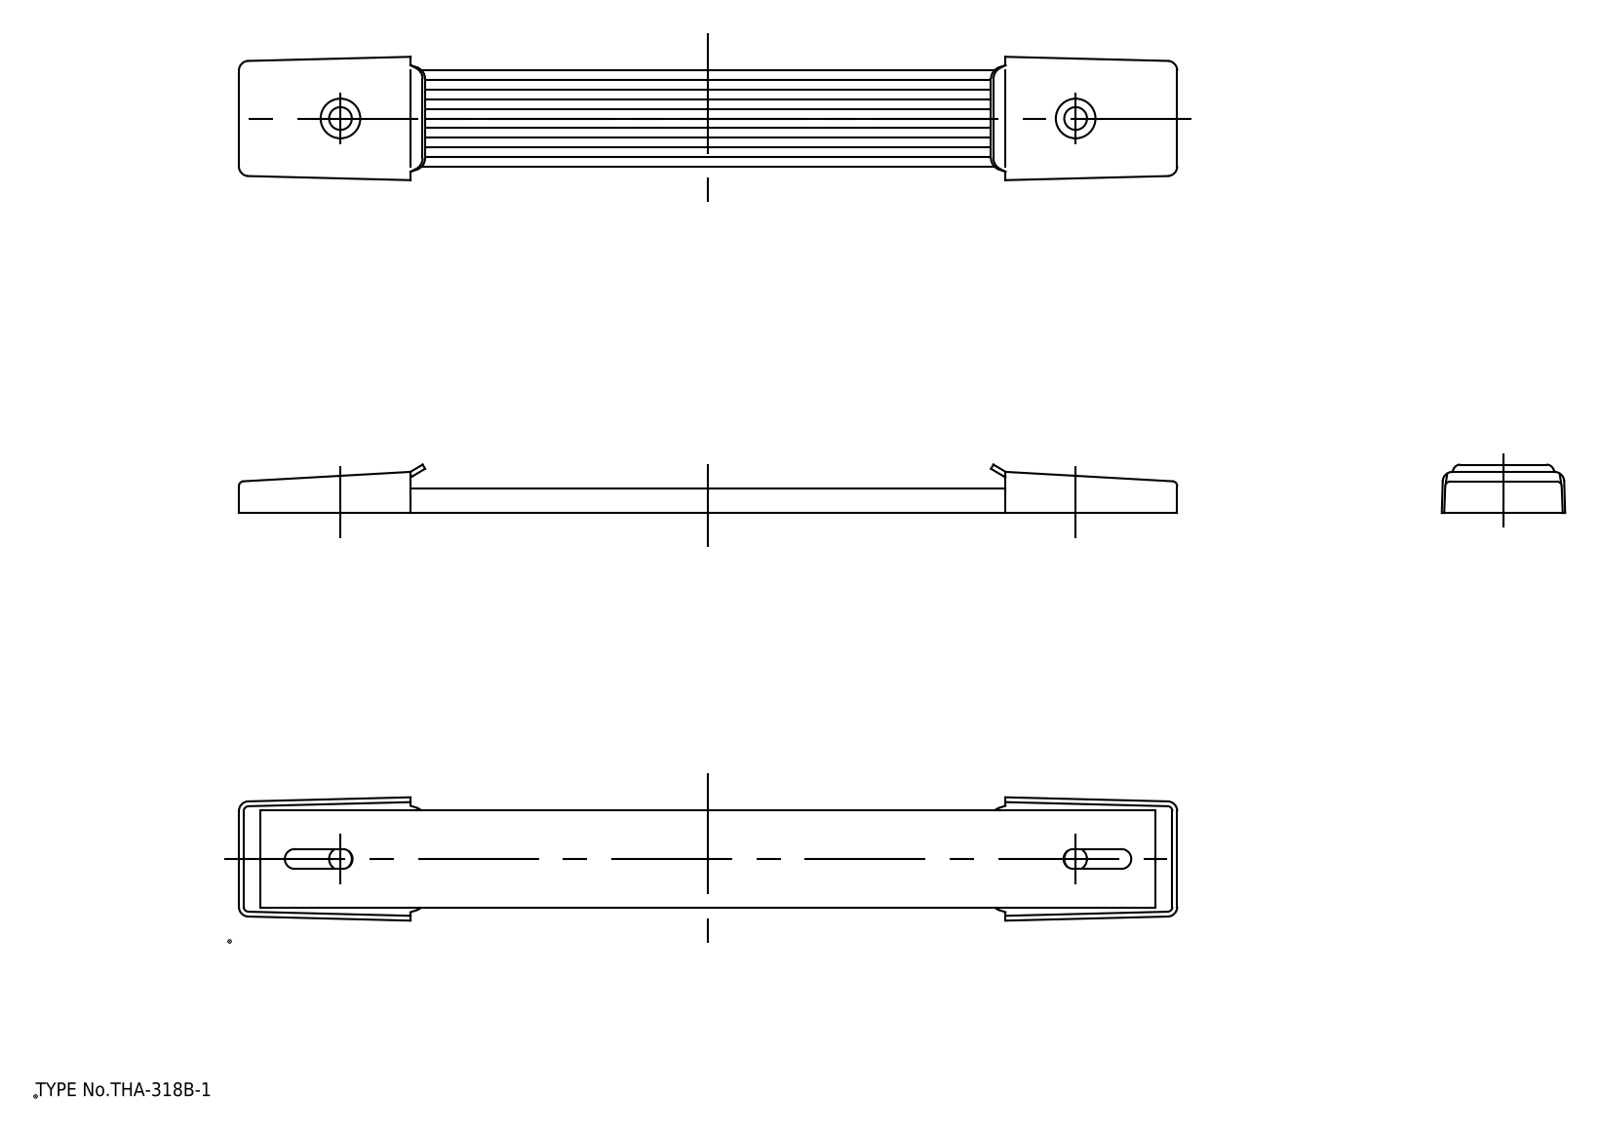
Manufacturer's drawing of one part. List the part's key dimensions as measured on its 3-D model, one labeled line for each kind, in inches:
Part name (STEP PRODUCT): bracket; leaf spring; grip
STEP written by: spGate 19.8.4 (****-****-****-****) (AUTOMOTIVE_DESIGN)
Units: inches
Bodies: 4 solids, 116 faces (56 planar, 44 cylindrical, 16 other)
Overall size (bounding box): 7.638 × 1.004 × 0.394
Volume: 1.127 in³ · Surface area: 40.97 in²
Round holes (diameter × count): ⌀0.185 ×2, ⌀0.323 ×2
Partial cylindrical surfaces — rounded edges, fillets, slot ends (radius × count): R0.039 ×12, R0.098 ×6, R0.079 ×4, R0.081 ×4, R0.02 ×2
Main face-to-face distances: 0.079, 0.089, 0.108, 0.118, 0.03, 0.039, 0.197, 0.02, 1.085, 1.086
Hole centre spacings: 5.984
